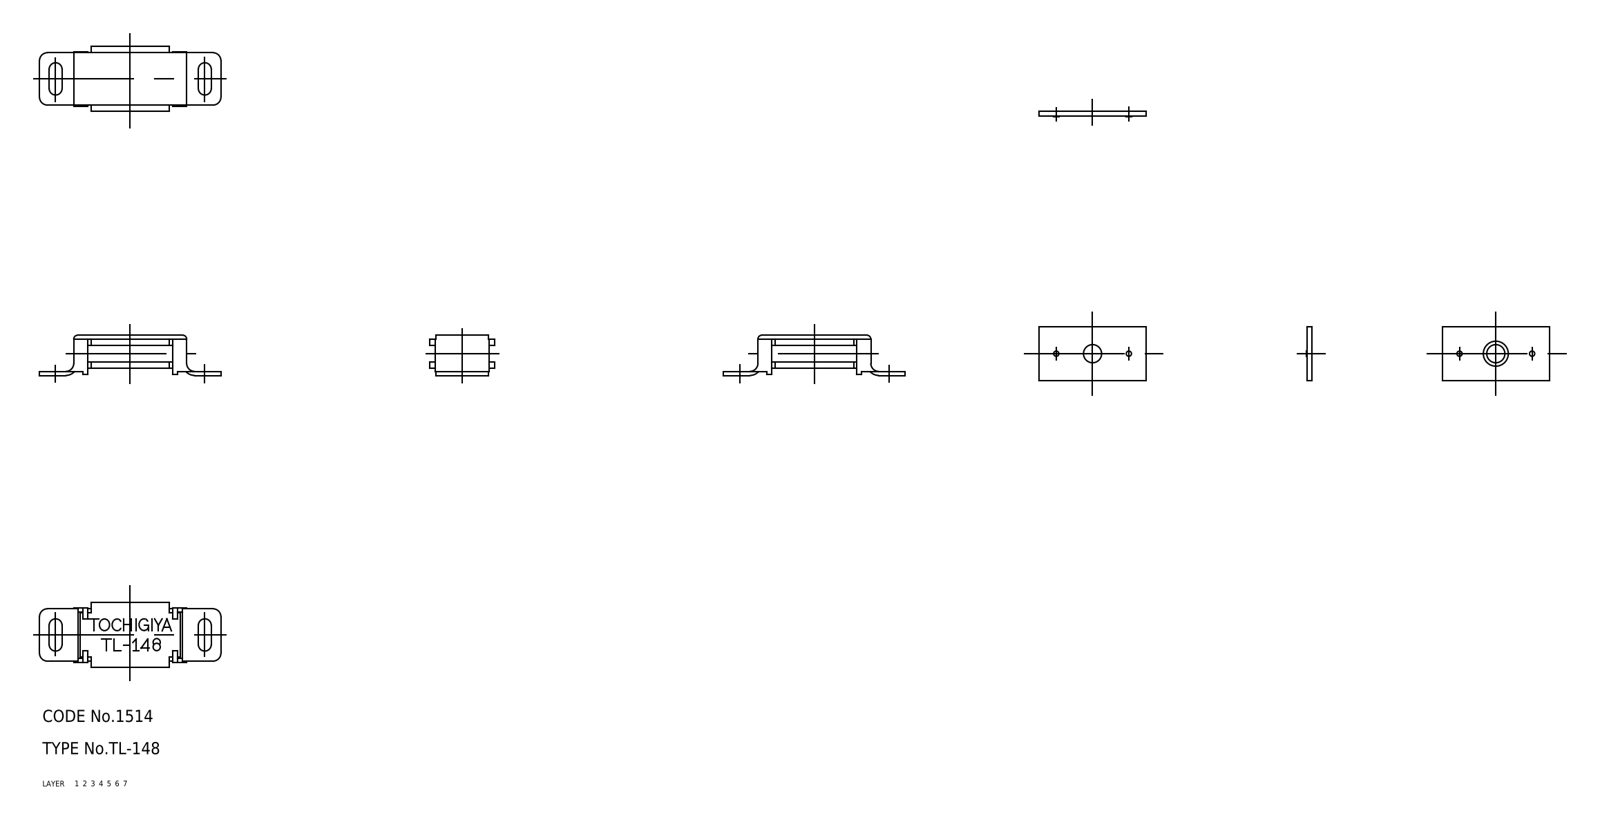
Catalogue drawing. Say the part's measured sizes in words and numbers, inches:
The part is named "attachment; magnet; keeper; housing (+1 more)". Its 3-D file was written by "CADfix (AUTOMOTIVE_DESIGN)". It is 5 solids with 136 faces: 0 planar, 0 cylindrical and 136 other. Overall it measures 1.772 by 1.246 by 0.531 inches. Its volume is 0.215 cubic inches and its surface area 8.156 square inches.
